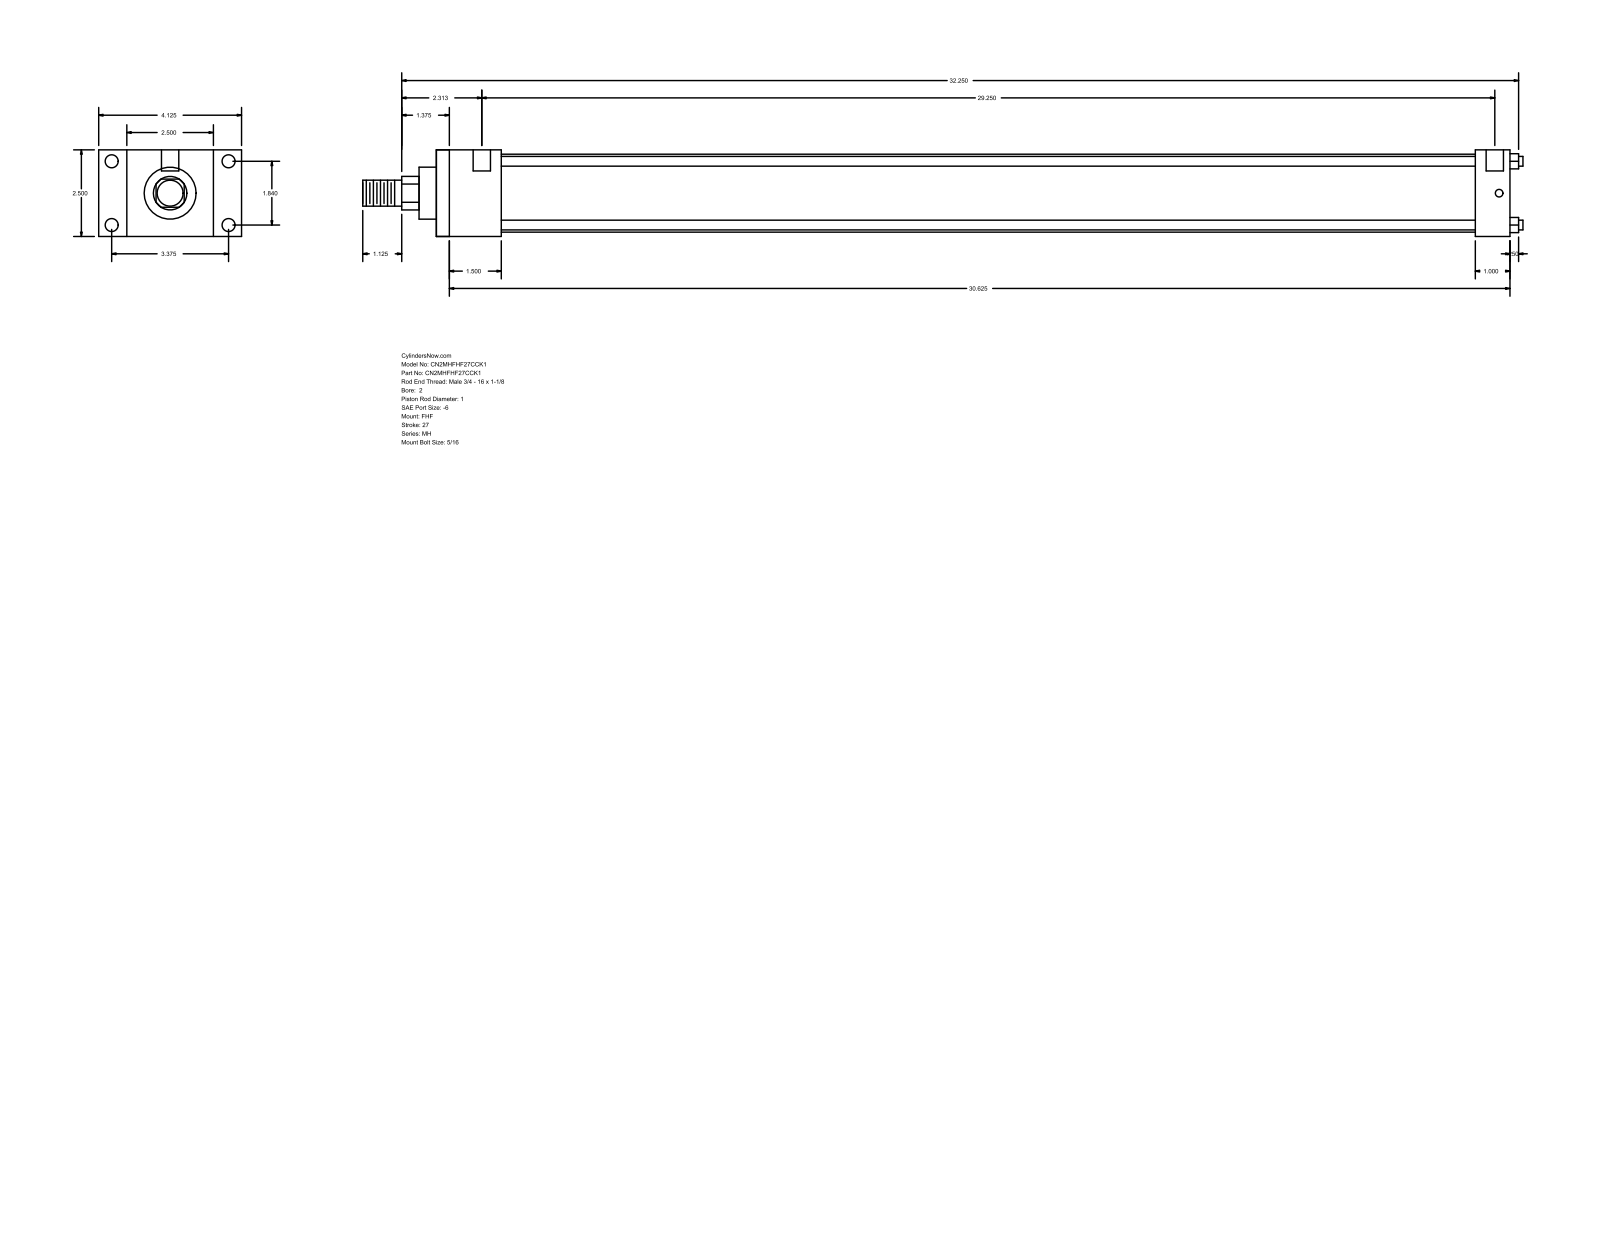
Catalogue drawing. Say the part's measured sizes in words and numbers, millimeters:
The part is named "MH_FHF__0200_1". Its 3-D file was written by "GSSL Pune (CONFIG_CONTROL_DESIGN)". It is 0 solids with 88 faces: 60 planar, 28 cylindrical and 0 other. Overall it measures 850.9 by 104.78 by 63.5 millimeters. Round holes: 4 of diameter 5.56, 4 of diameter 9.53, 2 of diameter 12.7. Round bosses or shafts: 4 of diameter 7.14, 1 of diameter 57.15, 1 of diameter 38.1, 1 of diameter 25.4, 1 of diameter 19.05. Partial cylindrical surfaces (rounded edges, fillets, slot ends): 1 of radius 12.29. The main face-to-face distances are 63.5, 787.4, 47.63, 739.77, 20.64, 84.14, 104.78, 25.4, 762, 714.37. The hole center spacings are 46.74, 85.72, 97.63, 750.88, 3.17, 4.76, 742.95, 746.12.
